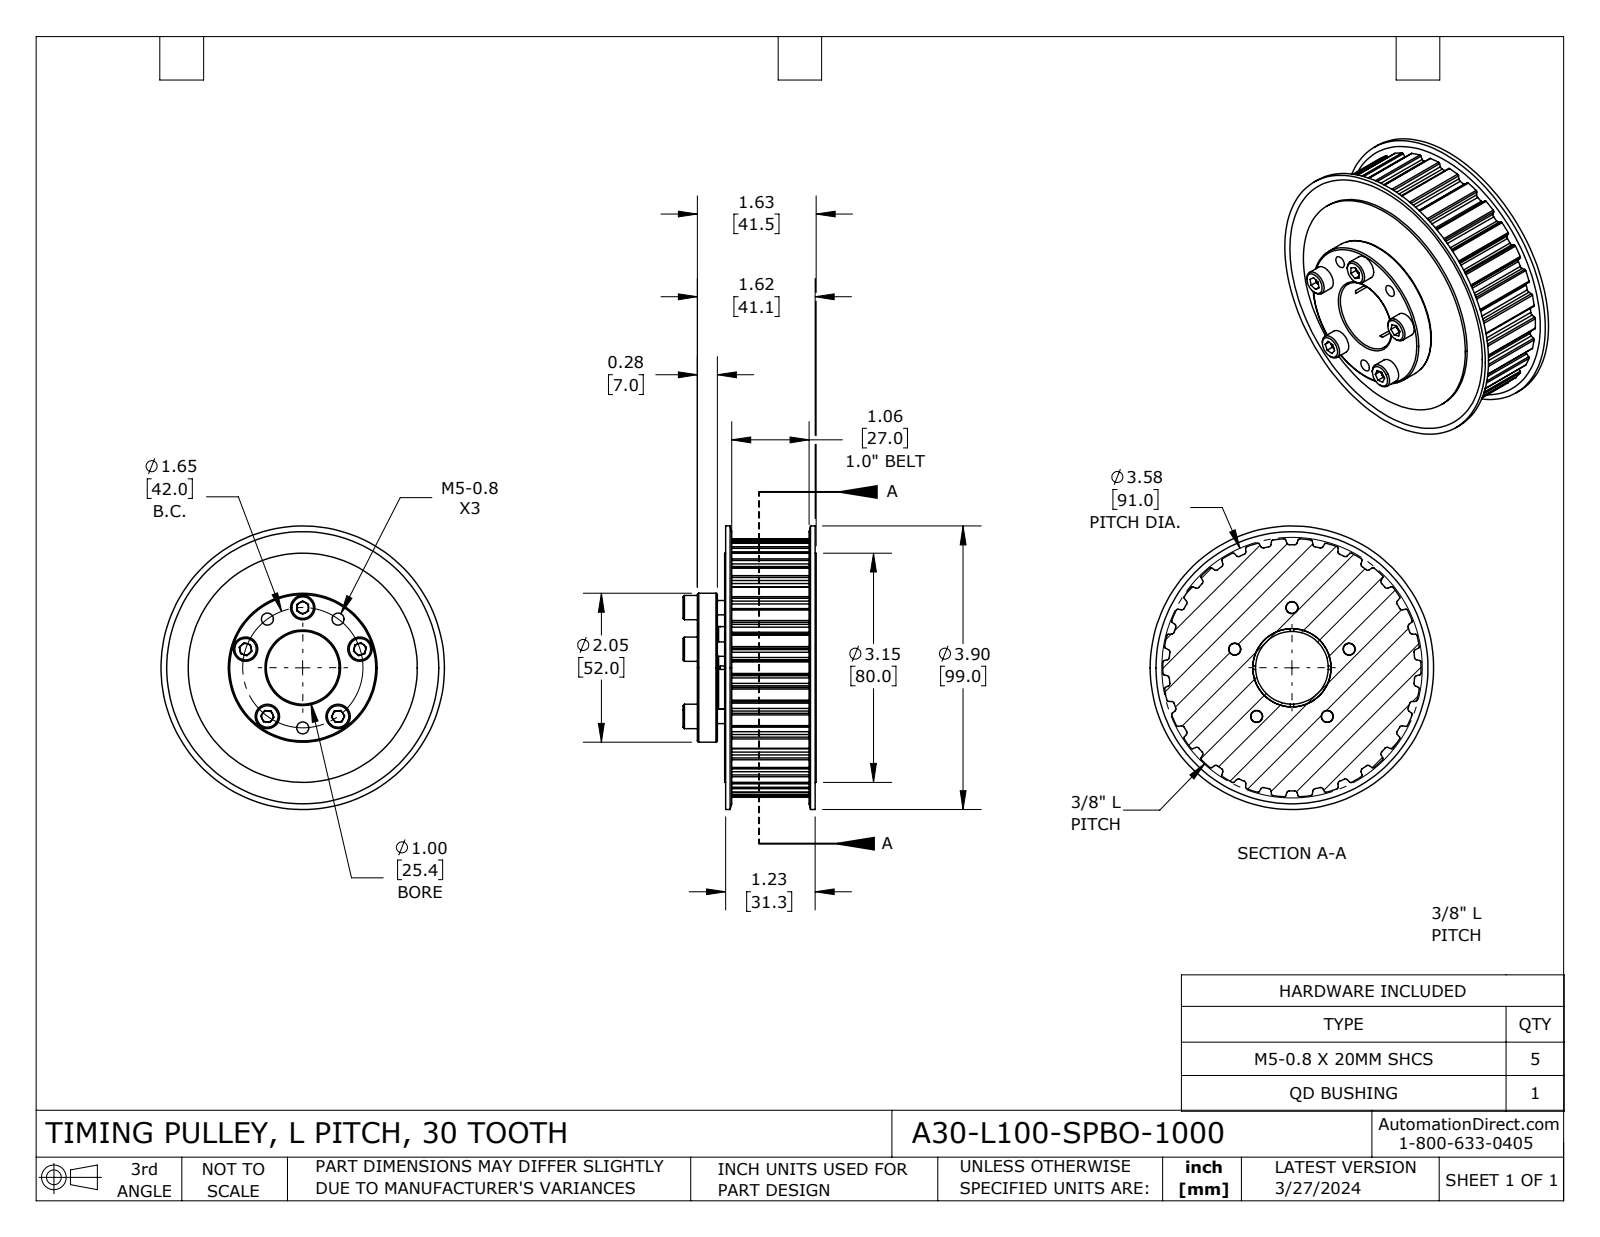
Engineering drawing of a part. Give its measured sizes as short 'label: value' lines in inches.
name: A30-L100-SPBO-1000
written by: SolidWorks 2021 (CONFIG_CONTROL_DESIGN)
unit: in
bodies: 9 solids, 504 faces (161 planar, 273 cylindrical, 70 other)
size: 3.898 × 3.898 × 1.831
volume: 11.93 in³; area: 76.42 in²
holes: 8× ⌀0.165, 5× ⌀0.217, 1× ⌀1, 1× ⌀1.134, 1× ⌀3.15
bosses: 5× ⌀0.335, 5× ⌀0.197, 1× ⌀3.898, 1× ⌀2.047
rounds: 60× R0.021, 60× R0.034, 1× R1.692, 1× R1.776
face distances: 0.098, 1.161, 1.26, 0.035, 1.224, 0.063, 1.126, 1.063, 1.189, 0.472
hole spacings: 0.827, 1.572, 0.511, 0.972, 1.338, 1.654, 0.972, 1.337
